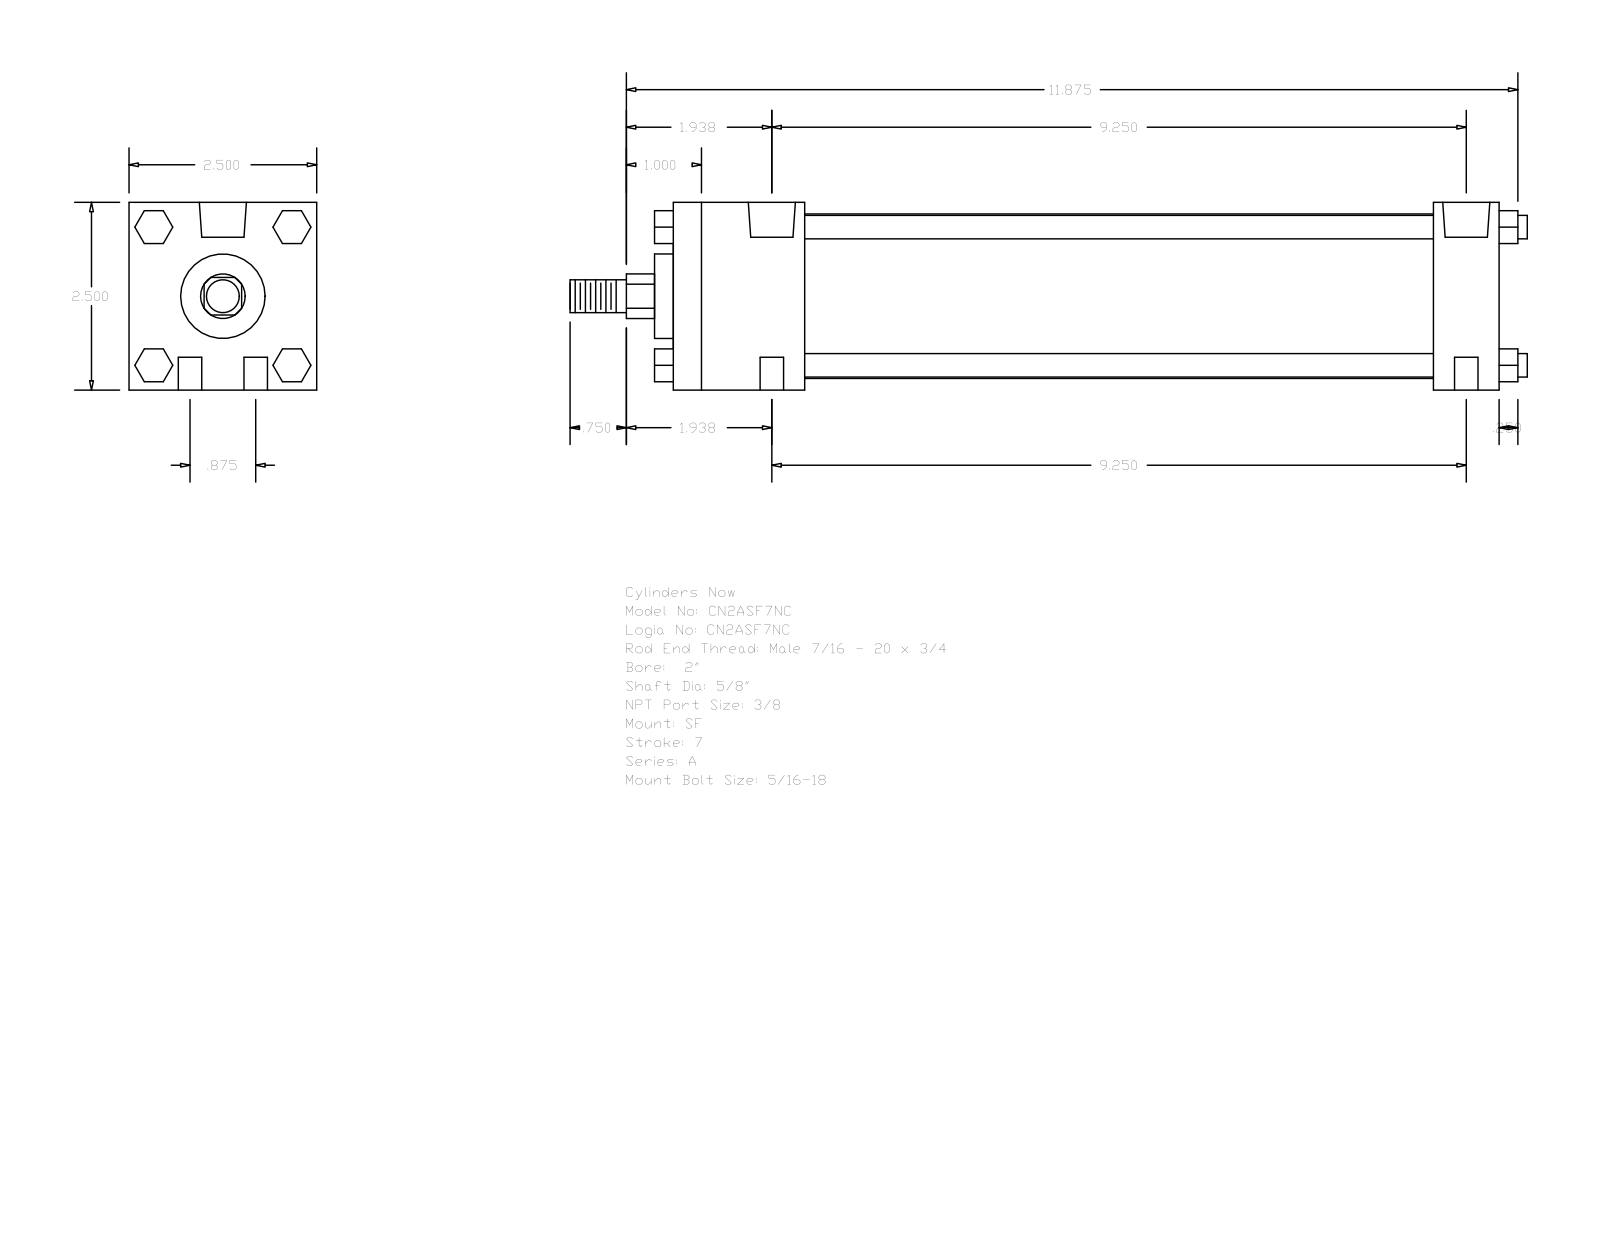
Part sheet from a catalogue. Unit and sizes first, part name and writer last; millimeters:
Units: millimetres
Overall size (bounding box): 323.85 × 63.5 × 63.5
Round holes (diameter × count): ⌀7.94 ×4, ⌀5.56 ×2, ⌀15.93 ×2
Round bosses / shafts (diameter × count): ⌀7.94 ×4, ⌀55.63 ×1, ⌀28.57 ×1, ⌀15.88 ×1, ⌀11.11 ×1
Partial cylindrical surfaces — rounded edges, fillets, slot ends (radius × count): R7.54 ×1
Main face-to-face distances: 63.5, 279.39, 257.17, 22.22, 44.45, 212.72, 234.94, 6.35, 285.74, 50.8
Hole centre spacings: 11.11, 235.21, 234.95, 22.22, 236, 227
Bodies: 0 solids, 124 faces (94 planar, 30 cylindrical, 0 other)
Part name (STEP PRODUCT): A_SF__0200_0.625
STEP written by: GSSL Pune (CONFIG_CONTROL_DESIGN)
